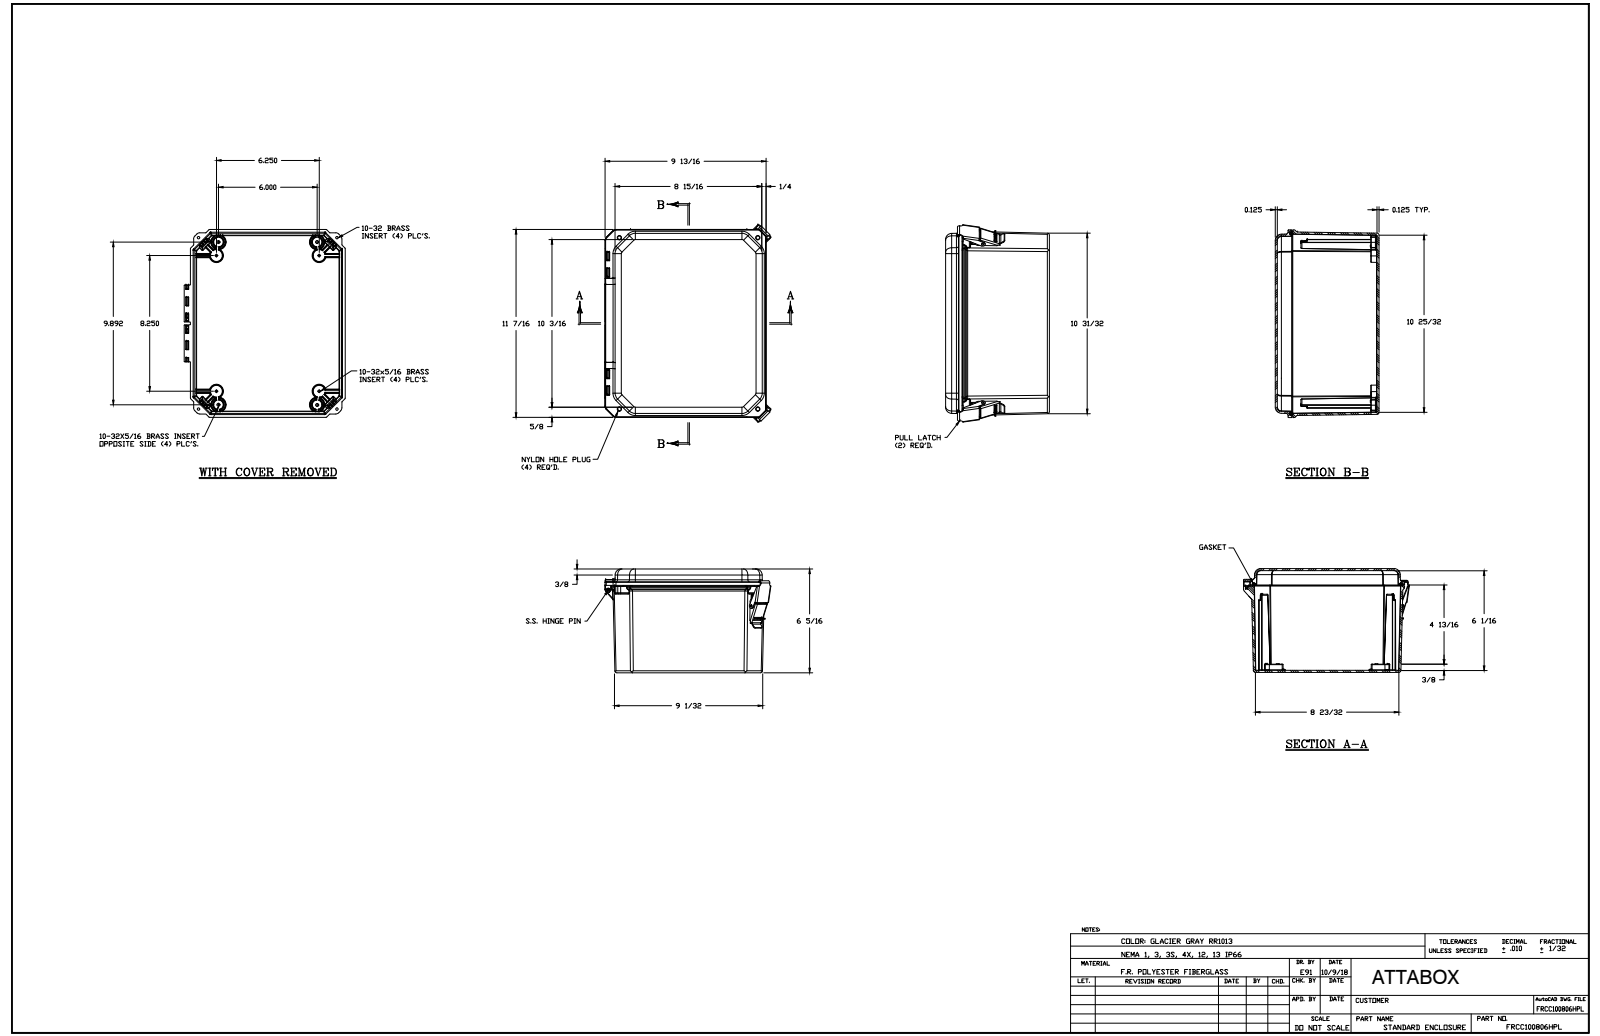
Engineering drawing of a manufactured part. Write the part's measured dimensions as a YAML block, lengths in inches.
part_name: "FRCC100806HPL"
step_written_by: "SolidWorks 2018 (AUTOMOTIVE_DESIGN)"
units: inches
bodies: {solids: 29, faces: 2200, planar: 656, cylindrical: 878, other: 666}
overall_size: [12.112, 10.147, 6.312]
volume: 62.99
surface_area: 981
round_holes:
  - {diameter: 0.156, count: 12}
  - {diameter: 0.135, count: 9}
  - {diameter: 0.152, count: 8}
  - {diameter: 0.15, count: 4}
  - {diameter: 0.219, count: 4}
  - {diameter: 0.252, count: 4}
  - {diameter: 0.312, count: 4}
  - {diameter: 0.135, count: 2}
  - {diameter: 0.137, count: 1}
  - {diameter: 0.375, count: 1}
  - {diameter: 0.375, count: 1}
round_bosses_or_shafts:
  - {diameter: 0.246, count: 12}
  - {diameter: 0.87, count: 4}
  - {diameter: 0.3, count: 4}
  - {diameter: 0.209, count: 4}
  - {diameter: 0.135, count: 1}
  - {diameter: 0.135, count: 1}
partial_cylinders:
  - {radius: 0.01, count: 188}
  - {radius: 0.005, count: 94}
  - {radius: 0.02, count: 59}
  - {radius: 0.03, count: 58}
  - {radius: 0.125, count: 29}
  - {radius: 0.09, count: 26}
  - {radius: 0.03, count: 24}
  - {radius: 0.06, count: 24}
face_to_face_distances: [0.125, 6.187, 0.127, 0.126, 6.312, 6.062, 0.656, 5.531, 0.25, 1]
hole_center_spacings: [0.25, 10.422, 0.831, 9.072, 9.399, 10.35, 11.873, 1.536]
